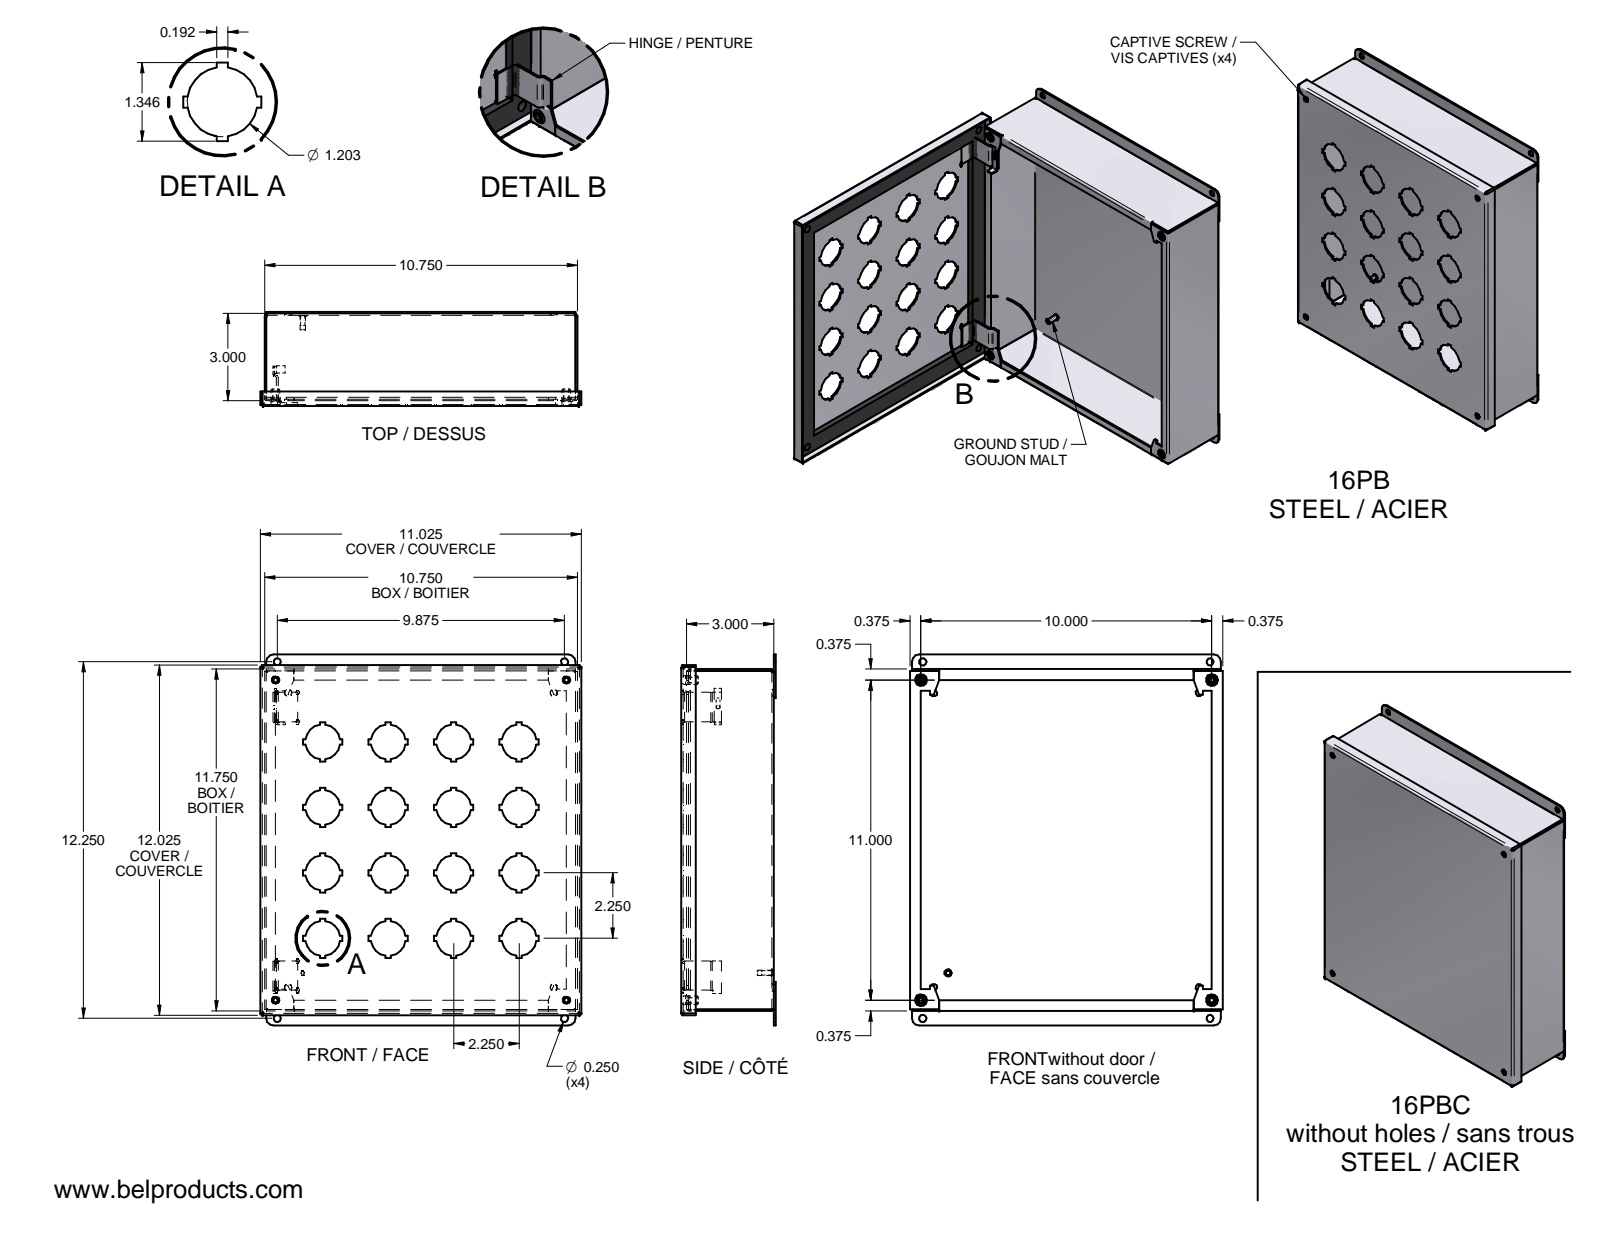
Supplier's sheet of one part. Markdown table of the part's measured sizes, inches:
| quantity | value |
| --- | --- |
| part name | 16PB_BOITIER; 10-32 x 0.500 AC_CD 201-008-772; INSERT 10-32 AVK ALS4-1032-130; 16PB-P (+7 more) |
| STEP written by | Unknown (AUTOMOTIVE_DESIGN) |
| units | inches |
| bodies | 9 solids, 1247 faces (884 planar, 91 cylindrical, 272 other) |
| overall size | 12.387 × 11.025 × 3.245 |
| volume | 34.44 in³ |
| surface area | 983.2 in² |
| round holes (diameter × count) | 0.125 × 9, 0.25 × 6, 0.245 × 4, 0.29 × 4, 0.312 × 4, 0.265 × 2, 0.136 × 1, 0.159 × 1, 0.216 × 1 |
| round bosses / shafts (diameter × count) | 0.119 × 9, 0.25 × 4, 0.296 × 1, 0.256 × 1, 0.19 × 1, 0.02 × 1 |
| partial cylindrical surfaces (radius × count) | 0.032 × 16, 0.092 × 16, 0.063 × 2, 0.25 × 2 |
| main face-to-face distances | 0.06, 3.125, 3.185, 3.065, 0.06, 10.69, 11.69, 10.63, 10.75, 0.137 |
| hole center spacings | 0.619, 0.736, 1.01, 1.25, 9.193, 9.222, 9.572, 10.572 |
